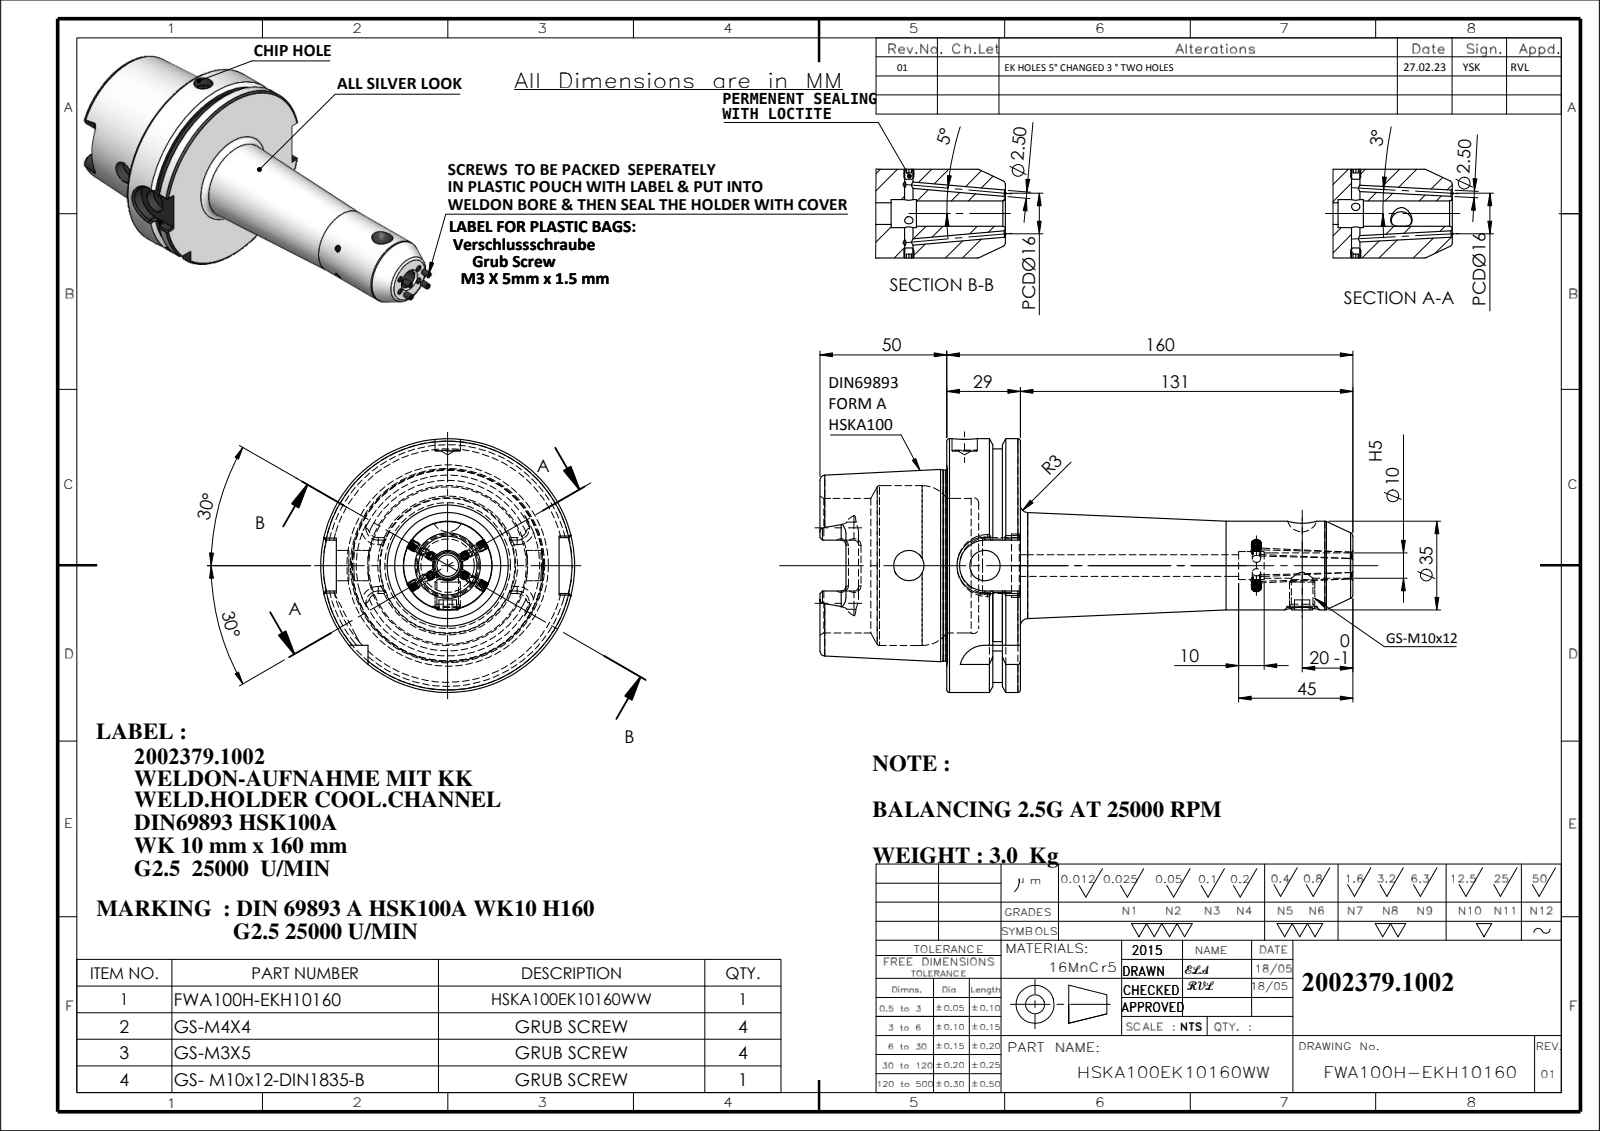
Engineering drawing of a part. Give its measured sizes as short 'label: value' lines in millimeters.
name: GS-M4X4_DIN 913 - M4 x 4-N; 91100A-WK10160; GS-M3X5; HSKA100EK10160WW (+1 more)
written by: SolidWorks 2018 (CONFIG_CONTROL_DESIGN)
unit: mm
bodies: 10 solids, 513 faces (155 planar, 126 cylindrical, 232 other)
size: 218.38 × 100 × 100
volume: 384 193 mm³; area: 70 776 mm²
holes: 4× ⌀2.5, 3× ⌀12, 2× ⌀3.3, 2× ⌀8.5, 2× ⌀10, 1× ⌀11, 1× ⌀21, 1× ⌀25, 1× ⌀53, 1× ⌀63
bosses: 4× ⌀3, 2× ⌀4, 1× ⌀100, 1× ⌀92, 1× ⌀75.16, 1× ⌀35, 1× ⌀10
rounds: 6× R1.8, 4× R4.88, 2× R10, 1× R11
face distances: 28.95, 12.5, 16.45, 50, 62.5, 78.95, 28.5, 78.5, 16, 0.45
hole spacings: 30, 133
